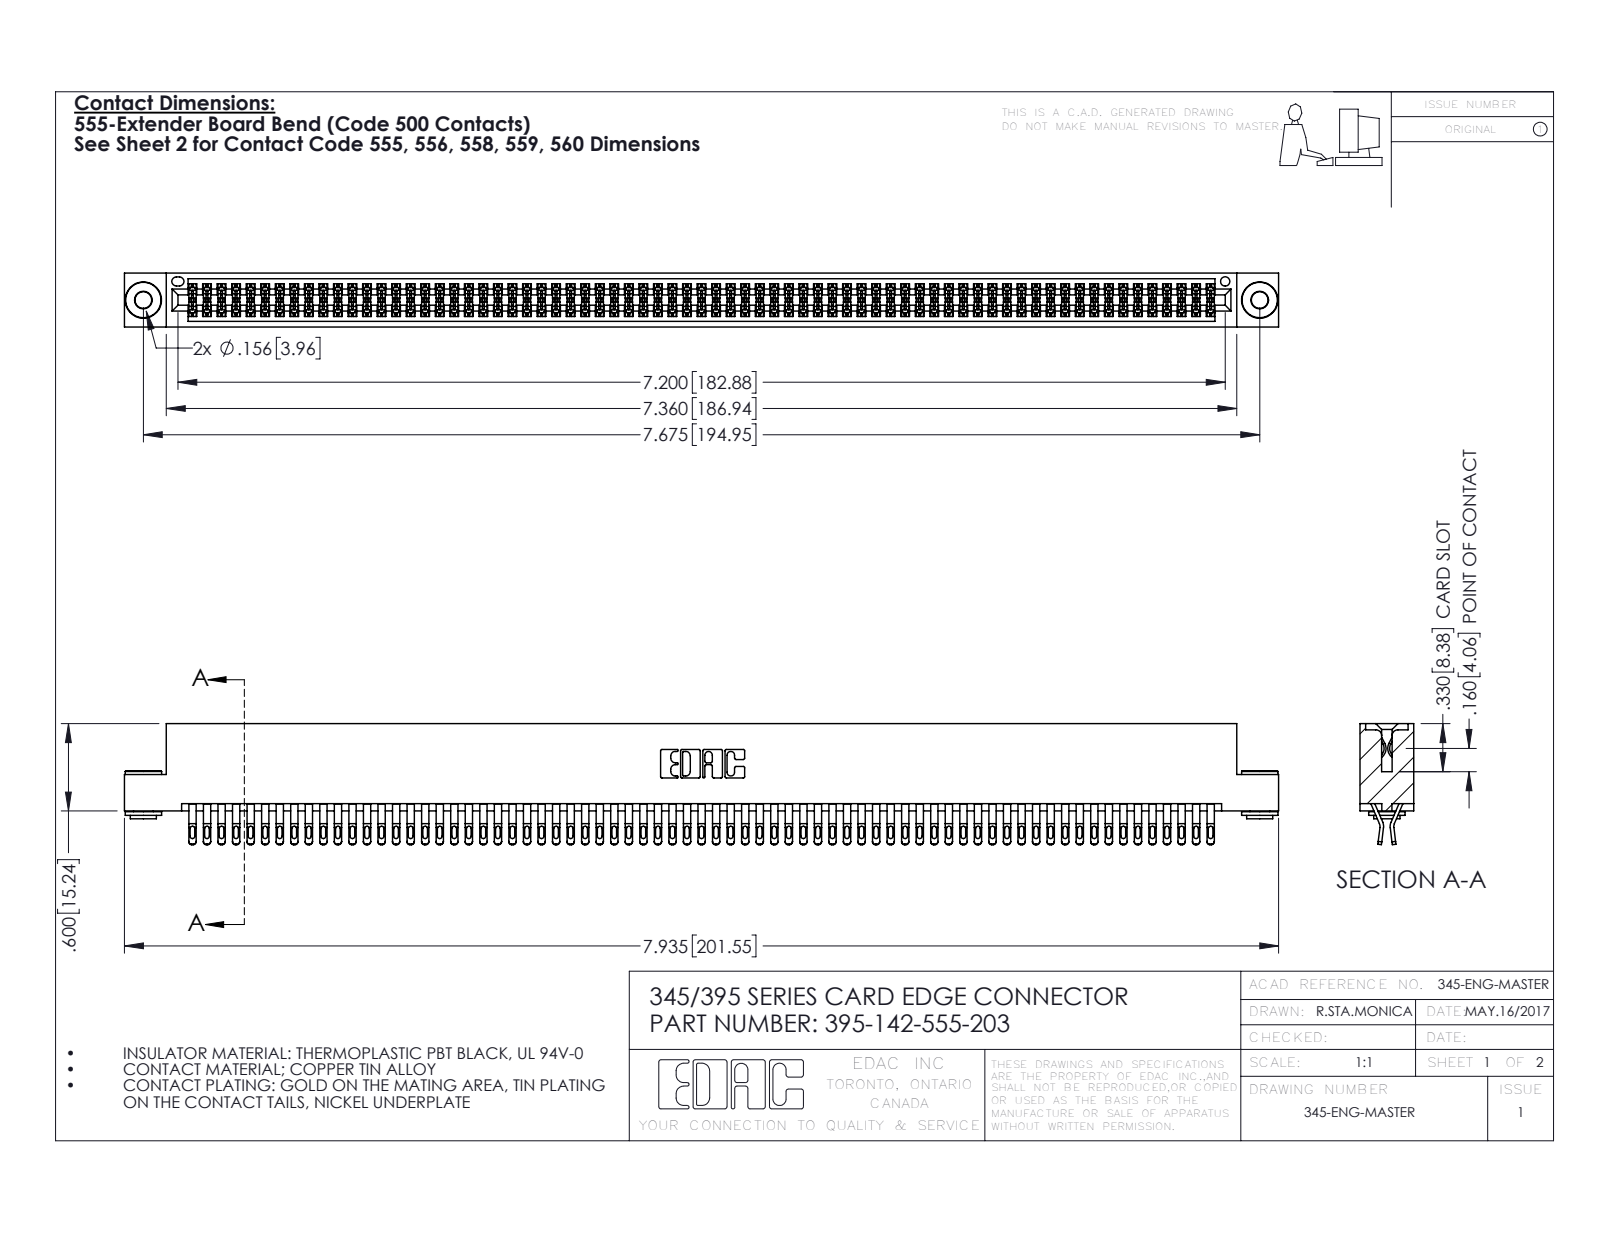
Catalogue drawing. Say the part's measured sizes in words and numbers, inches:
The part is named "345-292-001_555 Tail; 395-142-555-203; 345 Part_Flush Mounting Lugs - 0.156 Dia-TH; 345-250-002_345-250-002-102". Its 3-D file was written by "SolidWorks 2016 (CONFIG_CONTROL_DESIGN)". It is 145 solids with 8116 faces: 4492 planar, 3616 cylindrical and 8 other. Overall it measures 7.935 by 0.832 by 0.37 inches. Its volume is 1.238 cubic inches and its surface area 49.87 square inches. Round holes: 2 of diameter 0.116, 2 of diameter 0.156, 1 of diameter 0.064. Round bosses or shafts: 2 of diameter 0.25, 2 of diameter 0.18, 2 of diameter 0.136. Partial cylindrical surfaces (rounded edges, fillets, slot ends): 355 of radius 0.016, 284 of radius 0.02, 213 of radius 0.006, 22 of radius 0.01, 6 of radius 0.007, 6 of radius 0.031, 3 of radius 0.026, 2 of radius 0.01. The main face-to-face distances are 0.072, 0.298, 0.025, 0.2, 0.37, 0.098, 0.272, 0.225, 0.175, 0.149. The hole center spacings are 0.27, 7.439, 7.675.
